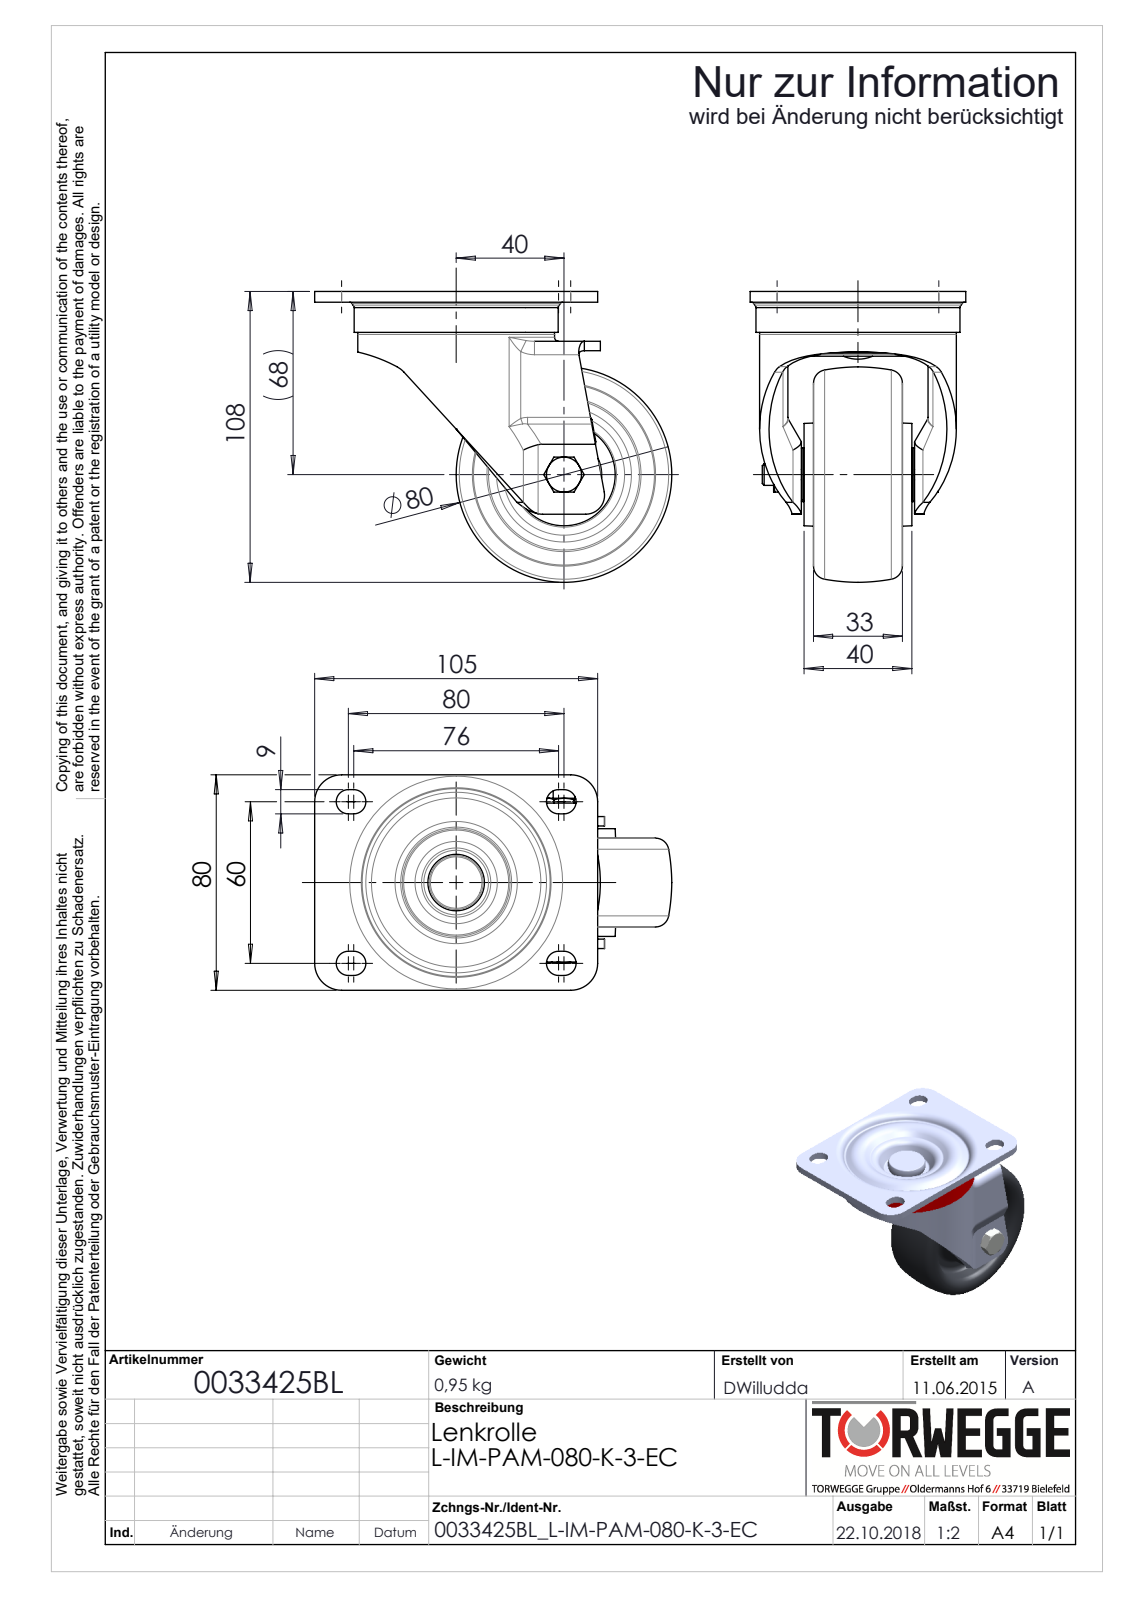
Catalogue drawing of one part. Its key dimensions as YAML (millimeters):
part_name: "0033425BL_L-IM-PAM-080-K-3-EC"
step_written_by: "SolidWorks 2016 (AUTOMOTIVE_DESIGN)"
units: millimeters
bodies: {solids: 20, faces: 787, planar: 339, cylindrical: 196, other: 252}
overall_size: [132.5, 108, 80]
volume: 237411
surface_area: 110237
round_holes:
  - {diameter: 6.8, count: 1}
  - {diameter: 8, count: 1}
  - {diameter: 8.2, count: 1}
  - {diameter: 12, count: 1}
  - {diameter: 12.4, count: 1}
  - {diameter: 12.5, count: 1}
  - {diameter: 16.8, count: 1}
  - {diameter: 23, count: 1}
  - {diameter: 23.2, count: 1}
  - {diameter: 35.1, count: 1}
  - {diameter: 35.5, count: 1}
  - {diameter: 46.75, count: 1}
round_bosses_or_shafts:
  - {diameter: 75.69, count: 1}
  - {diameter: 73, count: 1}
  - {diameter: 52.5, count: 1}
  - {diameter: 28, count: 1}
  - {diameter: 21, count: 1}
  - {diameter: 20, count: 1}
  - {diameter: 15, count: 1}
  - {diameter: 13, count: 1}
partial_cylinders:
  - {radius: 0.27, count: 8}
  - {radius: 4.5, count: 8}
  - {radius: 0.15, count: 7}
  - {radius: 0.45, count: 7}
  - {radius: 0.63, count: 4}
  - {radius: 0.68, count: 4}
  - {radius: 1.5, count: 4}
  - {radius: 5, count: 4}
face_to_face_distances: [4, 3.5, 1, 5, 50.5, 14, 41, 1.5, 20.05, 8]
